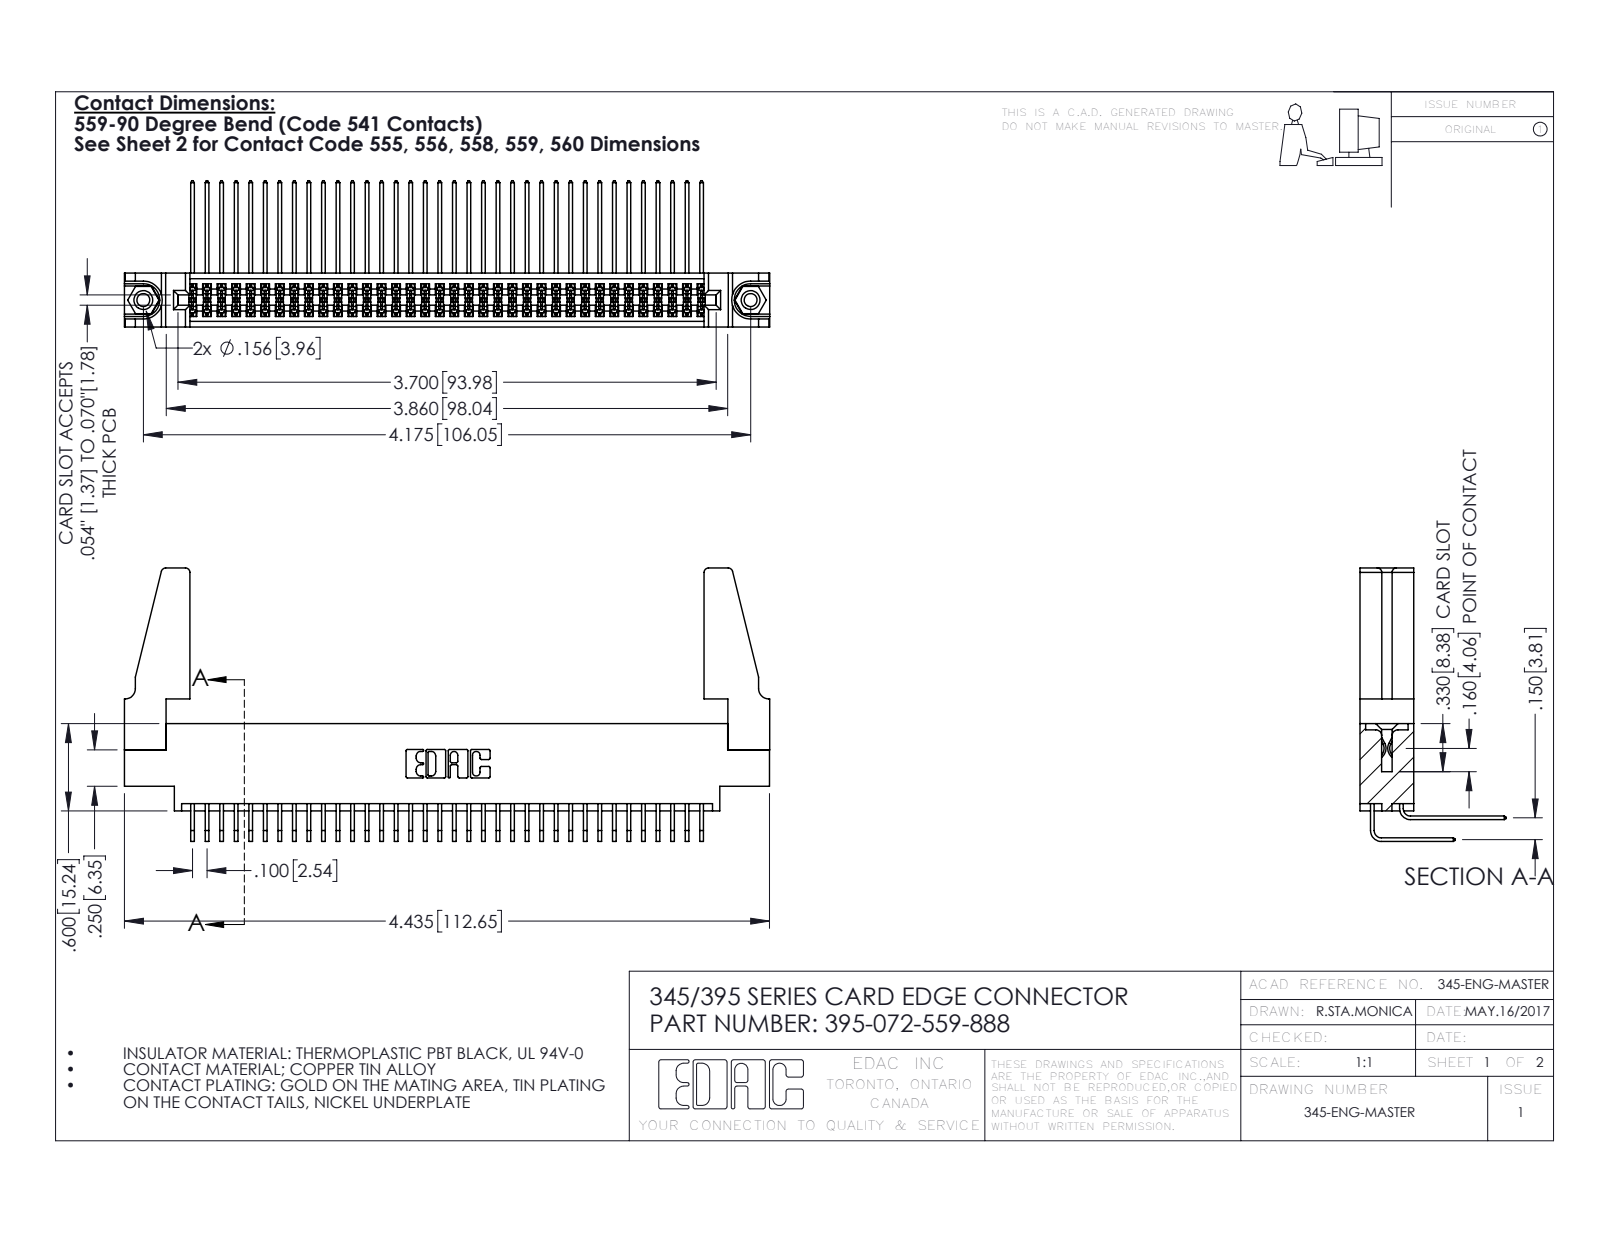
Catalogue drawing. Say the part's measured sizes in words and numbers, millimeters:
The part is named "345-292-001_558 559 Tail - 1; 345-250-001_345-250-001-102; 345-220-078_345-220-088; 395-072-559-888 (+2 more)". Its 3-D file was written by "SolidWorks 2016 (CONFIG_CONTROL_DESIGN)". It is 77 solids with 3998 faces: 2676 planar, 1306 cylindrical and 16 other. Overall it measures 112.7 by 47.7 by 25.5 millimeters. Its volume is 14 400 cubic millimeters and its surface area 21 650 square millimeters. Round holes: 2 of diameter 2.3, 2 of diameter 3.2, 2 of diameter 4, 1 of diameter 1.6. Round bosses or shafts: 2 of diameter 3.9. Partial cylindrical surfaces (rounded edges, fillets, slot ends): 108 of radius 0.2, 22 of radius 0.3, 8 of radius 0.8, 6 of radius 0.2, 6 of radius 0.8, 3 of radius 0.7, 2 of radius 0.4, 2 of radius 0.5. The main face-to-face distances are 1.8, 7.6, 9.4, 5.1, 2.5, 6.9, 0.6, 5.7, 3.8, 4.4. The hole center spacings are 6.9, 100.1, 106.
